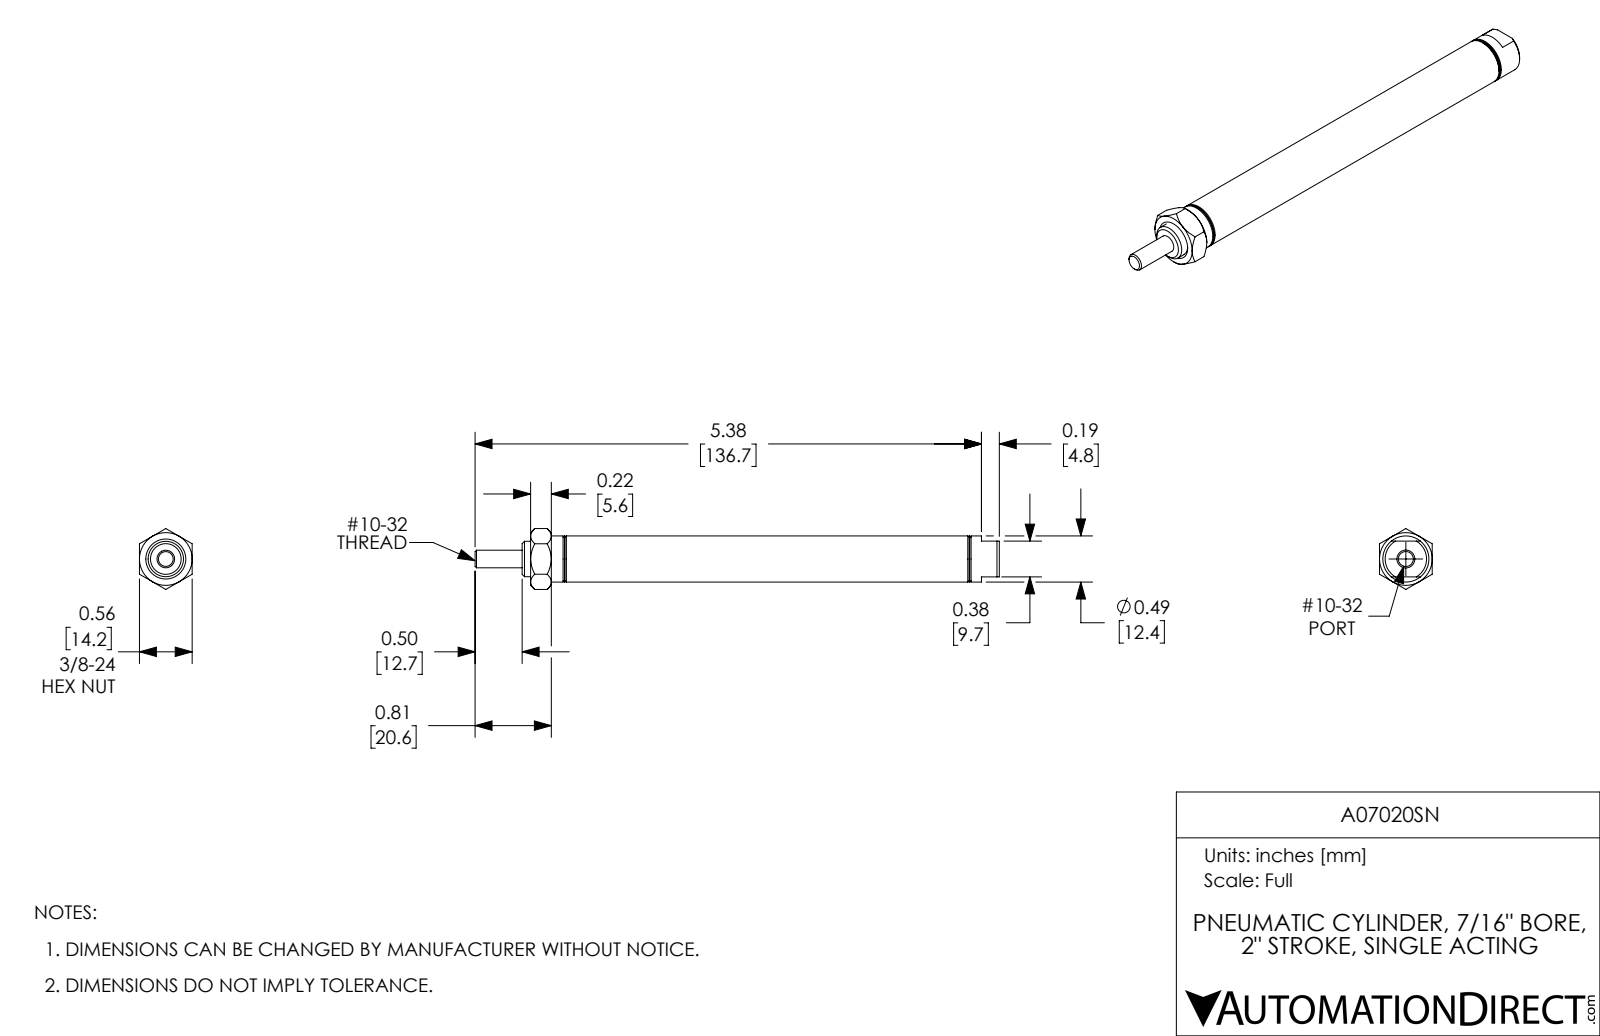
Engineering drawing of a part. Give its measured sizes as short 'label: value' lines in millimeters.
name: A07020SN_Mounting Nut_D-801; A07020SN-MainBody; A07020SN; A07020SN-Rod
written by: SolidWorks 2017 (AUTOMOTIVE_DESIGN)
unit: mm
bodies: 3 solids, 84 faces (25 planar, 26 cylindrical, 33 other)
size: 141.5 × 16.4 × 14.2
volume: 11 700 mm³; area: 11 110 mm²
holes: 1× ⌀4, 1× ⌀4.7, 1× ⌀4.8, 1× ⌀9.5, 1× ⌀11.1
bosses: 1× ⌀12.4, 1× ⌀9.6
face distances: 14.2, 92.2, 12.7, 79.5, 63.5, 50.8, 28.7, 28.7, 41.4, 92.2
